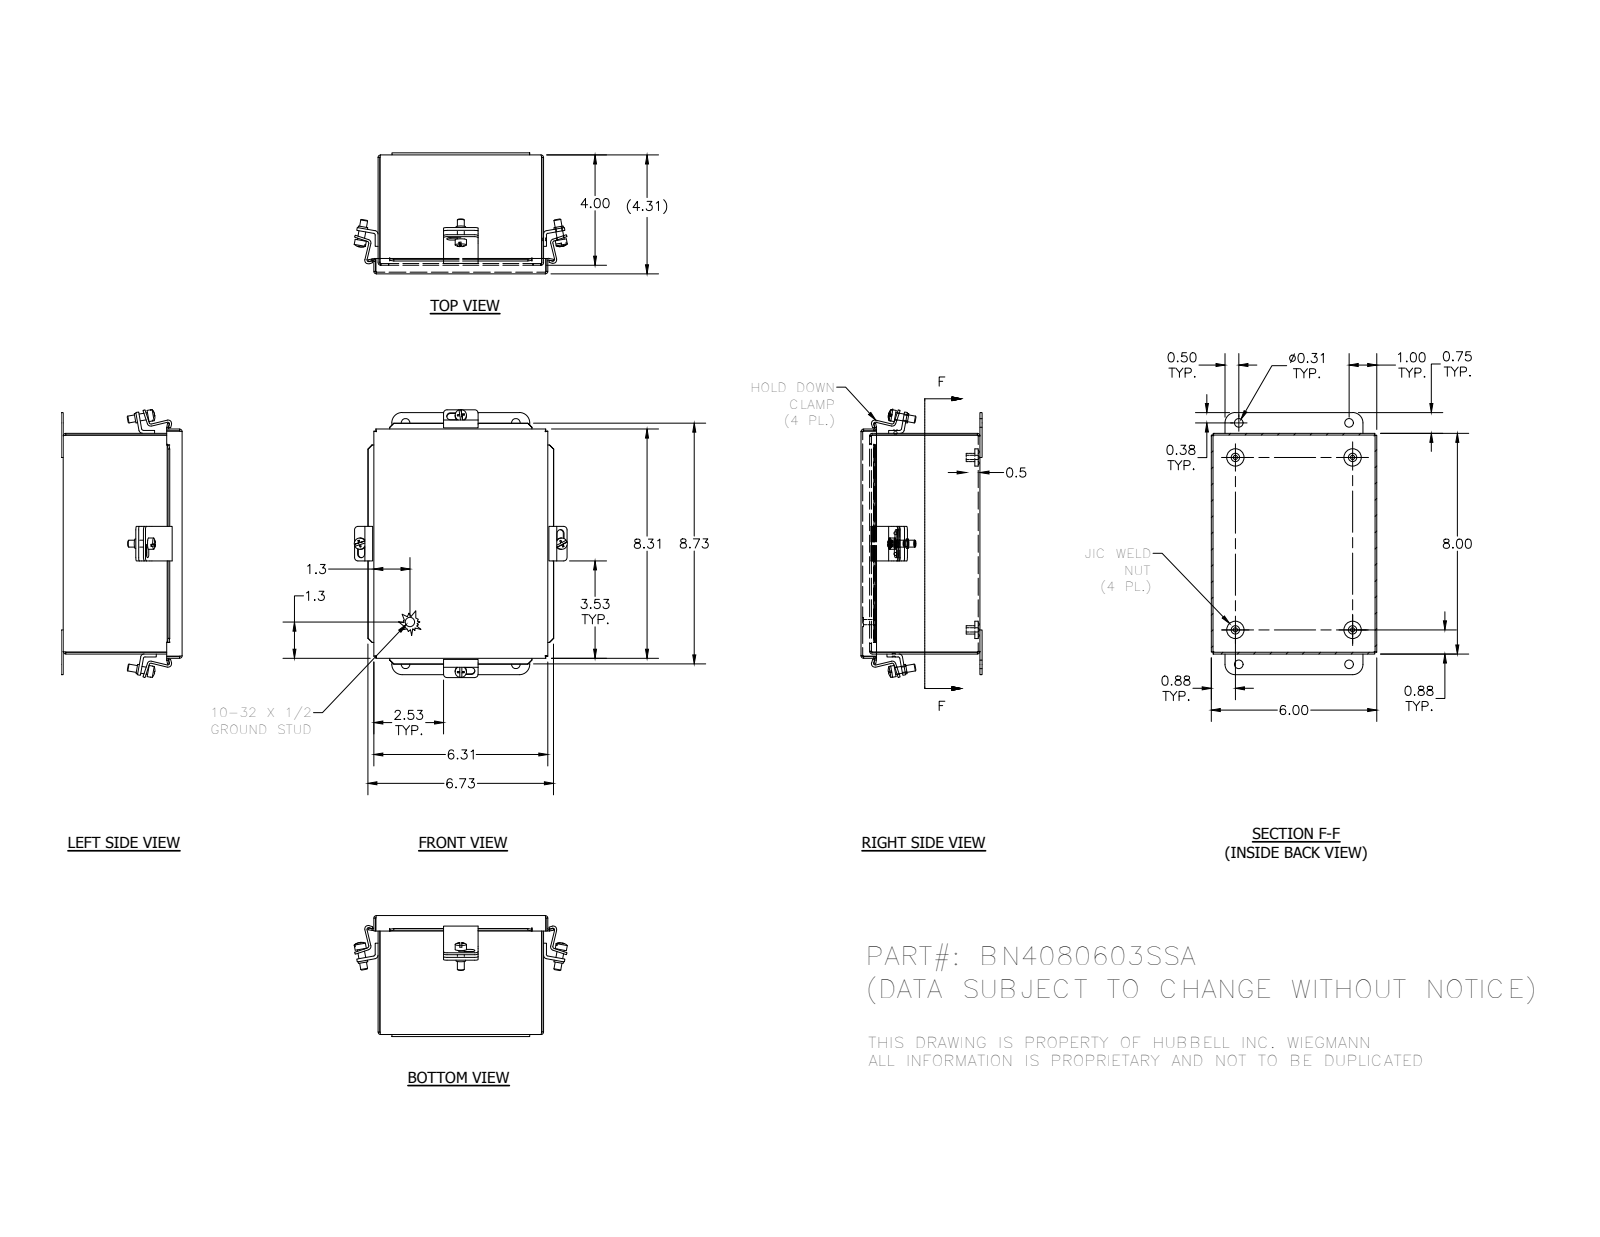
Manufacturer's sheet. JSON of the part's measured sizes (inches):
{"part_name": "372164_1; HFW3883; BN40806SSALID_1; BN4080604SSABKP_1 (+5 more)", "step_written_by": "SolidWorks 2014 (AUTOMOTIVE_DESIGN)", "units": "inches", "bodies": {"solids": 21, "faces": 589, "planar": 287, "cylindrical": 200, "other": 102}, "overall_size": [9.713, 7.724, 4.388], "volume_in3": 17.41, "surface_area_in2": 547.5, "round_holes": [[0.11, 6], [0.156, 4], [0.196, 4], [0.31, 4]], "round_bosses_or_shafts": [[0.625, 4], [0.41, 4], [0.344, 4], [0.3, 4], [0.25, 4], [0.337, 1], [0.19, 1]], "partial_cylinders_radius": [[0.031, 16], [0.094, 16], [0.125, 16], [0.063, 12], [0.126, 12], [0.133, 8], [0.375, 4]], "face_to_face_distances": [0.063, 4.25, 5.937, 4.313, 4.187, 7.937, 6, 5.875, 8, 7.875], "hole_center_spacings": [1.256, 4.31, 7.501, 8.559, 0.75, 0.063, 0.753, 4]}
